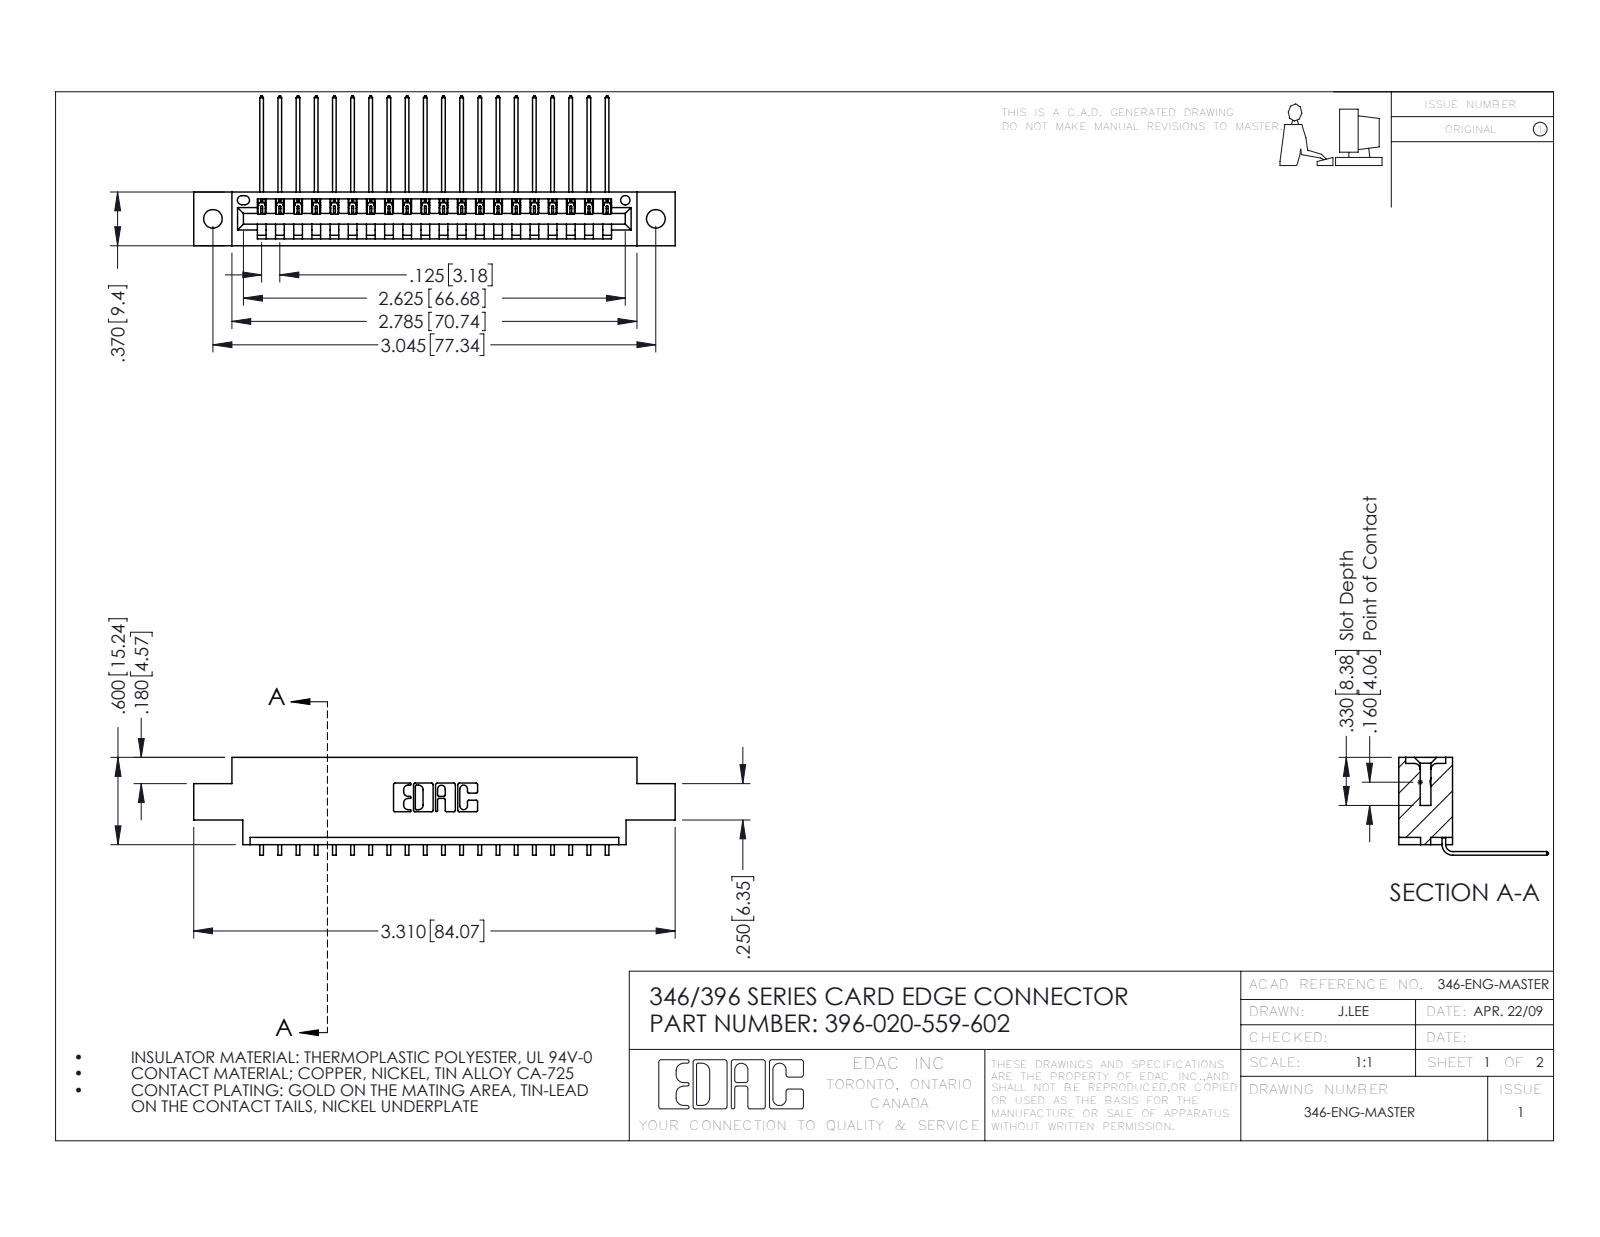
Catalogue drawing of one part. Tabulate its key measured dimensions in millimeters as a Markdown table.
| quantity | value |
| --- | --- |
| part name | 396-020-559-602; 346 Part_0.170 Offset - 0.128 Dia; 345-292-001_558 559 Tail - 1 |
| STEP written by | SolidWorks 2016 (CONFIG_CONTROL_DESIGN) |
| units | millimeters |
| bodies | 21 solids, 1326 faces (920 planar, 406 cylindrical, 0 other) |
| overall size | 84.1 × 26.2 × 17.1 |
| volume | 7 770 mm³ |
| surface area | 9 761 mm² |
| round holes (diameter × count) | 3.3 × 2, 1.6 × 1 |
| partial cylindrical surfaces (radius × count) | 0.2 × 40, 0.3 × 22, 0.2 × 6, 0.8 × 6, 0.7 × 3, 0.8 × 2, 1 × 2, 0.4 × 1 |
| main face-to-face distances | 1.2, 9.4, 8.2, 6.4, 0.6, 1.8, 3.8, 5.6, 2.5, 4.4 |
| hole center spacings | 6.2, 72.1, 77.3 |
